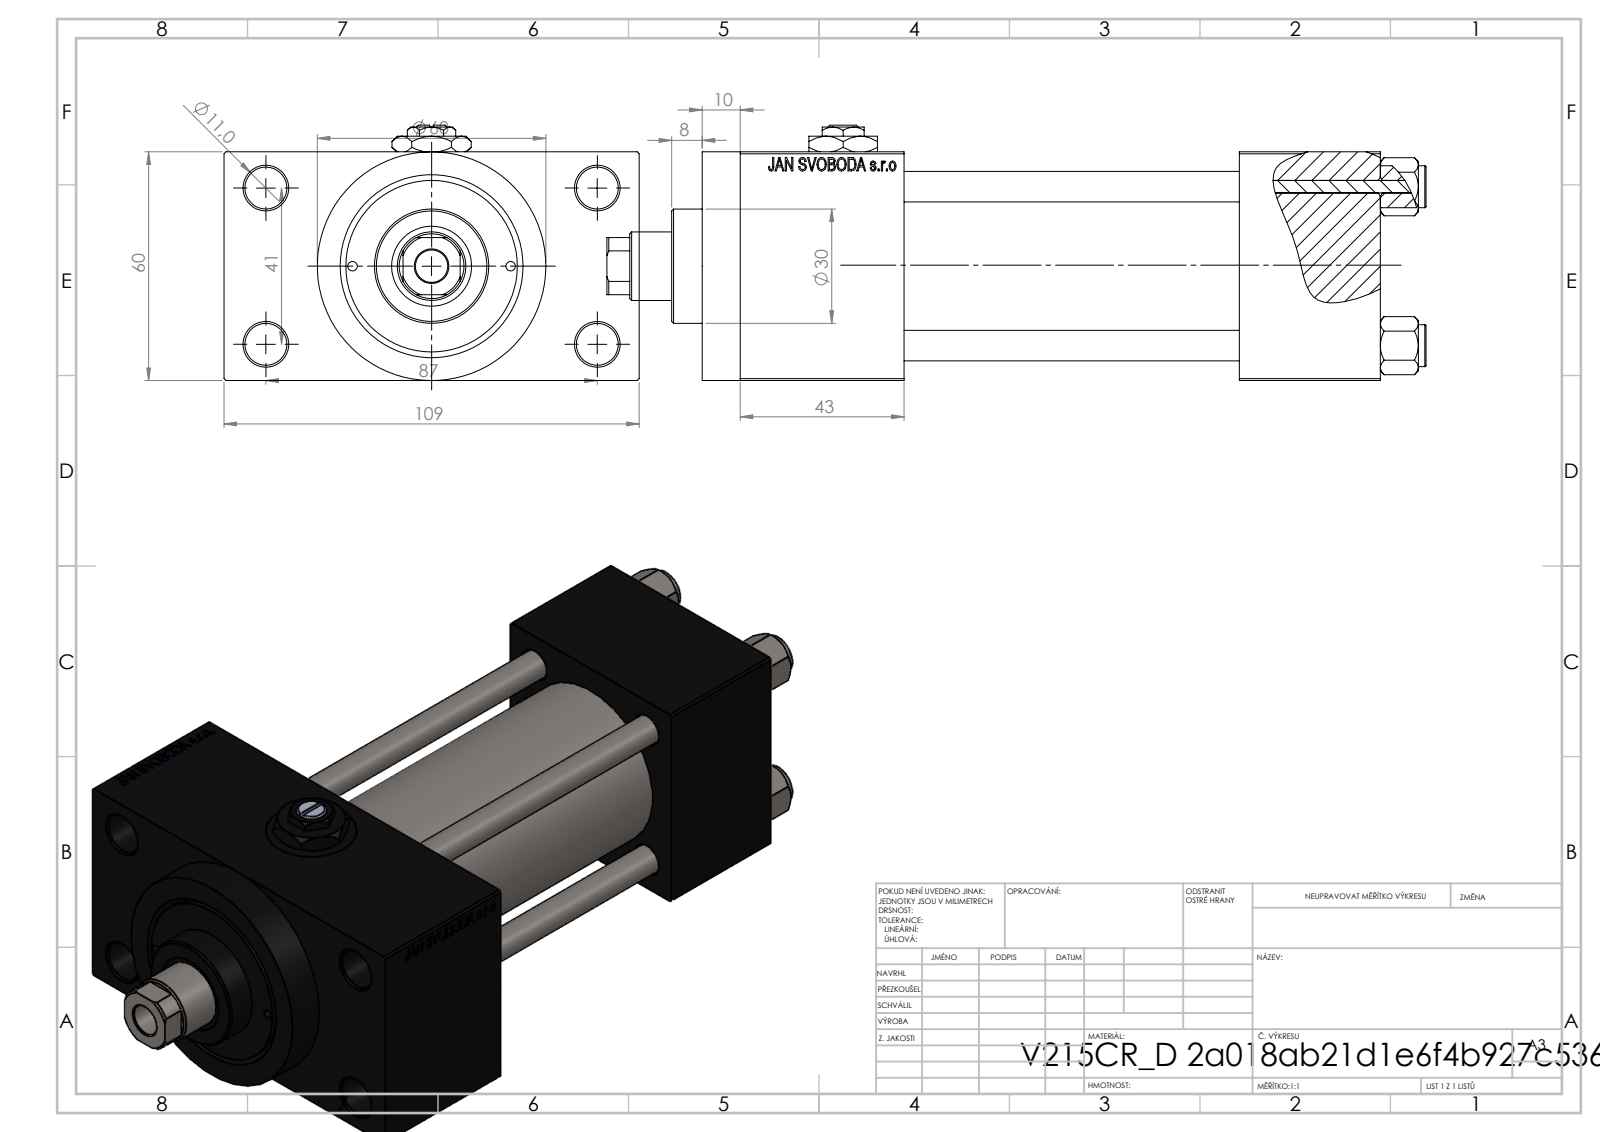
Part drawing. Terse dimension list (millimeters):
name: V215_VC_A; V215CR_D_Body; V215CR_VCP_D; NUT_M5_D (+2 more)
written by: SolidWorks 2019 (CONFIG_CONTROL_DESIGN)
unit: mm
bodies: 12 solids, 1160 faces (524 planar, 96 cylindrical, 540 other)
size: 215 × 109 × 67
volume: 537 701 mm³; area: 136 233 mm²
holes: 4× ⌀8, 4× ⌀11, 3× ⌀16.66, 3× ⌀24, 2× ⌀2.5, 2× ⌀7, 1× ⌀8.5, 1× ⌀18, 1× ⌀21, 1× ⌀31, 1× ⌀40, 1× ⌀45
bosses: 4× ⌀11, 1× ⌀60, 1× ⌀46, 1× ⌀30
rounds: 1× R8.5
face distances: 60, 88, 24.5, 84.5, 37, 125, 43, 168, 131, 10
hole spacings: 20.85, 22.65, 29.49, 30.62, 41.7, 46.53, 47.15, 48.09
